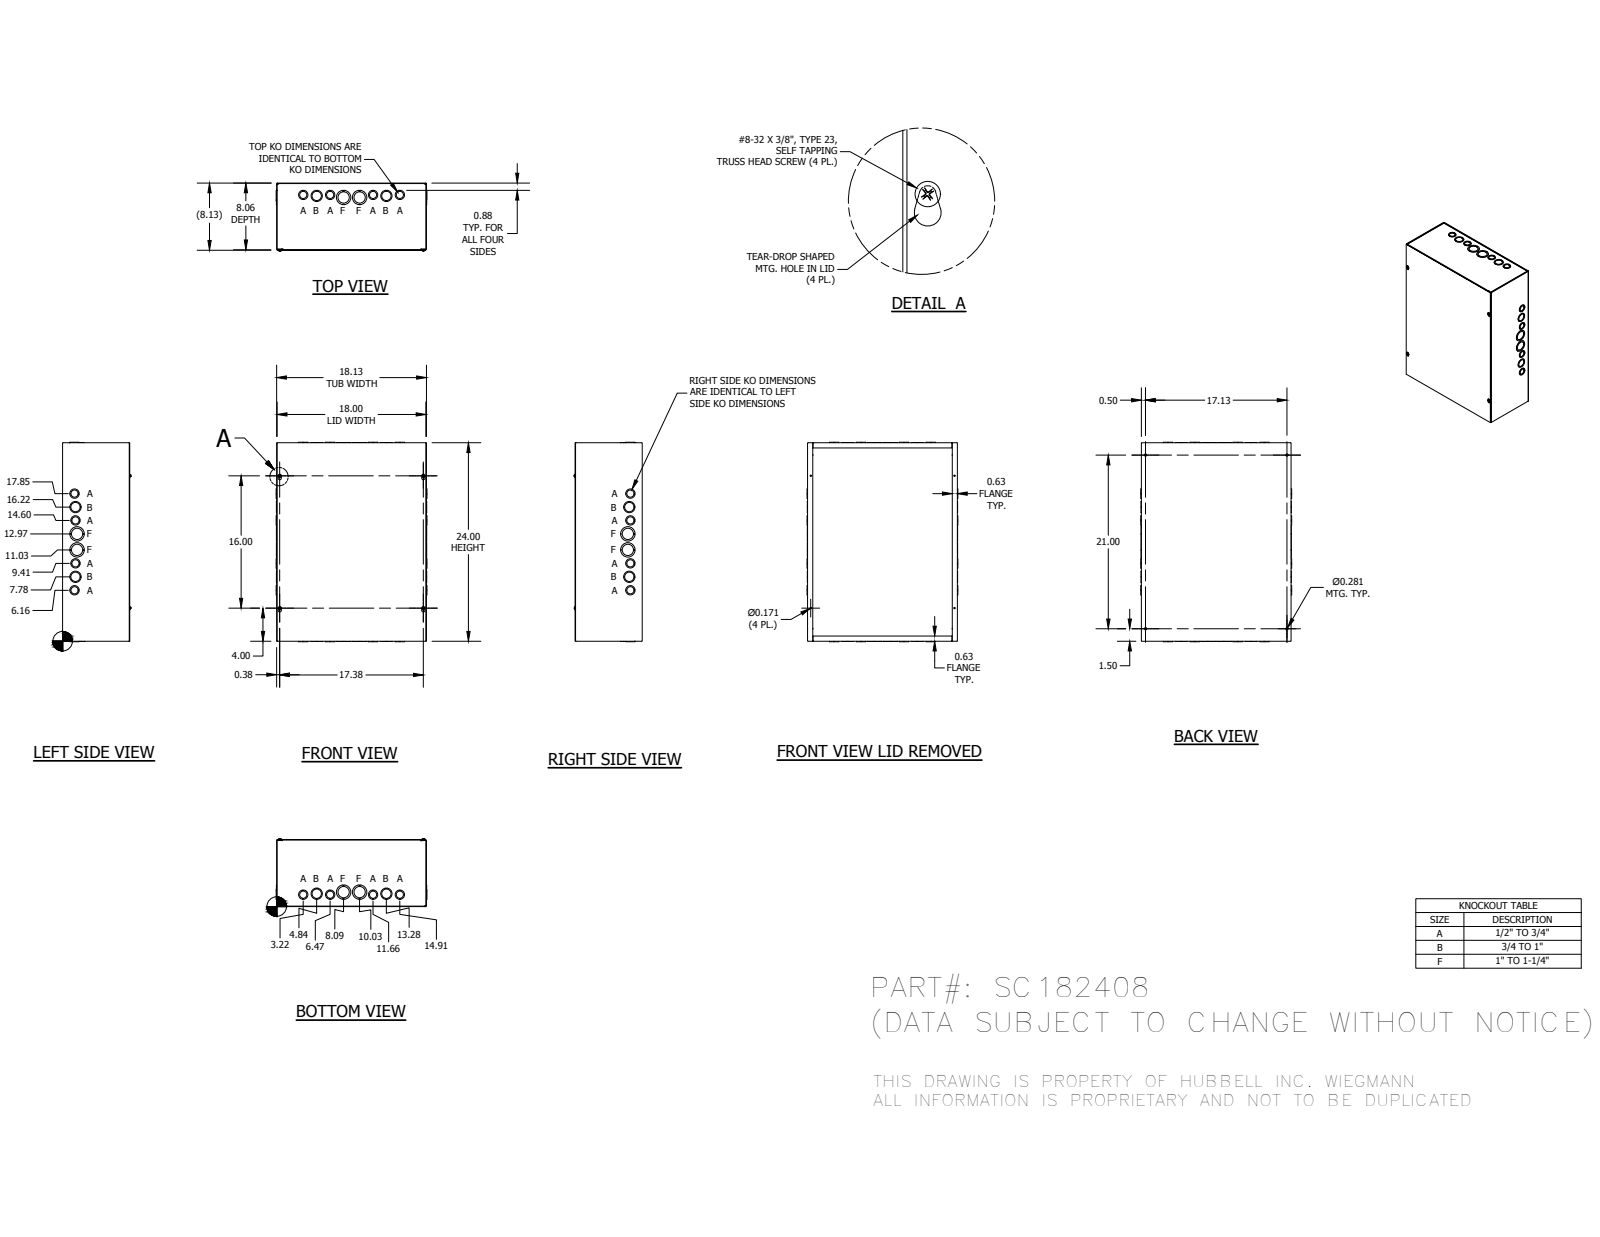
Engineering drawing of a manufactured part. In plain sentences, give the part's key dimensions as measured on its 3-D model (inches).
The part is named "SC182408BLR; SC1808TB; SC1824LPA; 34056 (+1 more)". Its 3-D file was written by "Autodesk Inventor 2014 (AUTOMOTIVE_DESIGN)". It is 37 solids with 1167 faces: 859 planar, 240 cylindrical and 68 other. Overall it measures 24.125 by 18.25 by 8.225 inches. Round holes: 14 of diameter 1.125, 10 of diameter 0.875, 8 of diameter 1.375, 4 of diameter 0.171, 4 of diameter 0.281, 4 of diameter 1.75. Round bosses or shafts: 4 of diameter 0.384, 4 of diameter 0.164. Partial cylindrical surfaces (rounded edges, fillets, slot ends): 12 of radius 0.031, 12 of radius 0.094, 4 of radius 0.125, 4 of radius 0.203. The main face-to-face distances are 0.063, 8.063, 8, 8.125, 18.063, 23.937, 18, 18.125, 24, 23.875. The hole center spacings are 1.63, 1.63, 1.655, 2.503, 3.25, 3.256, 3.579, 4.885.
